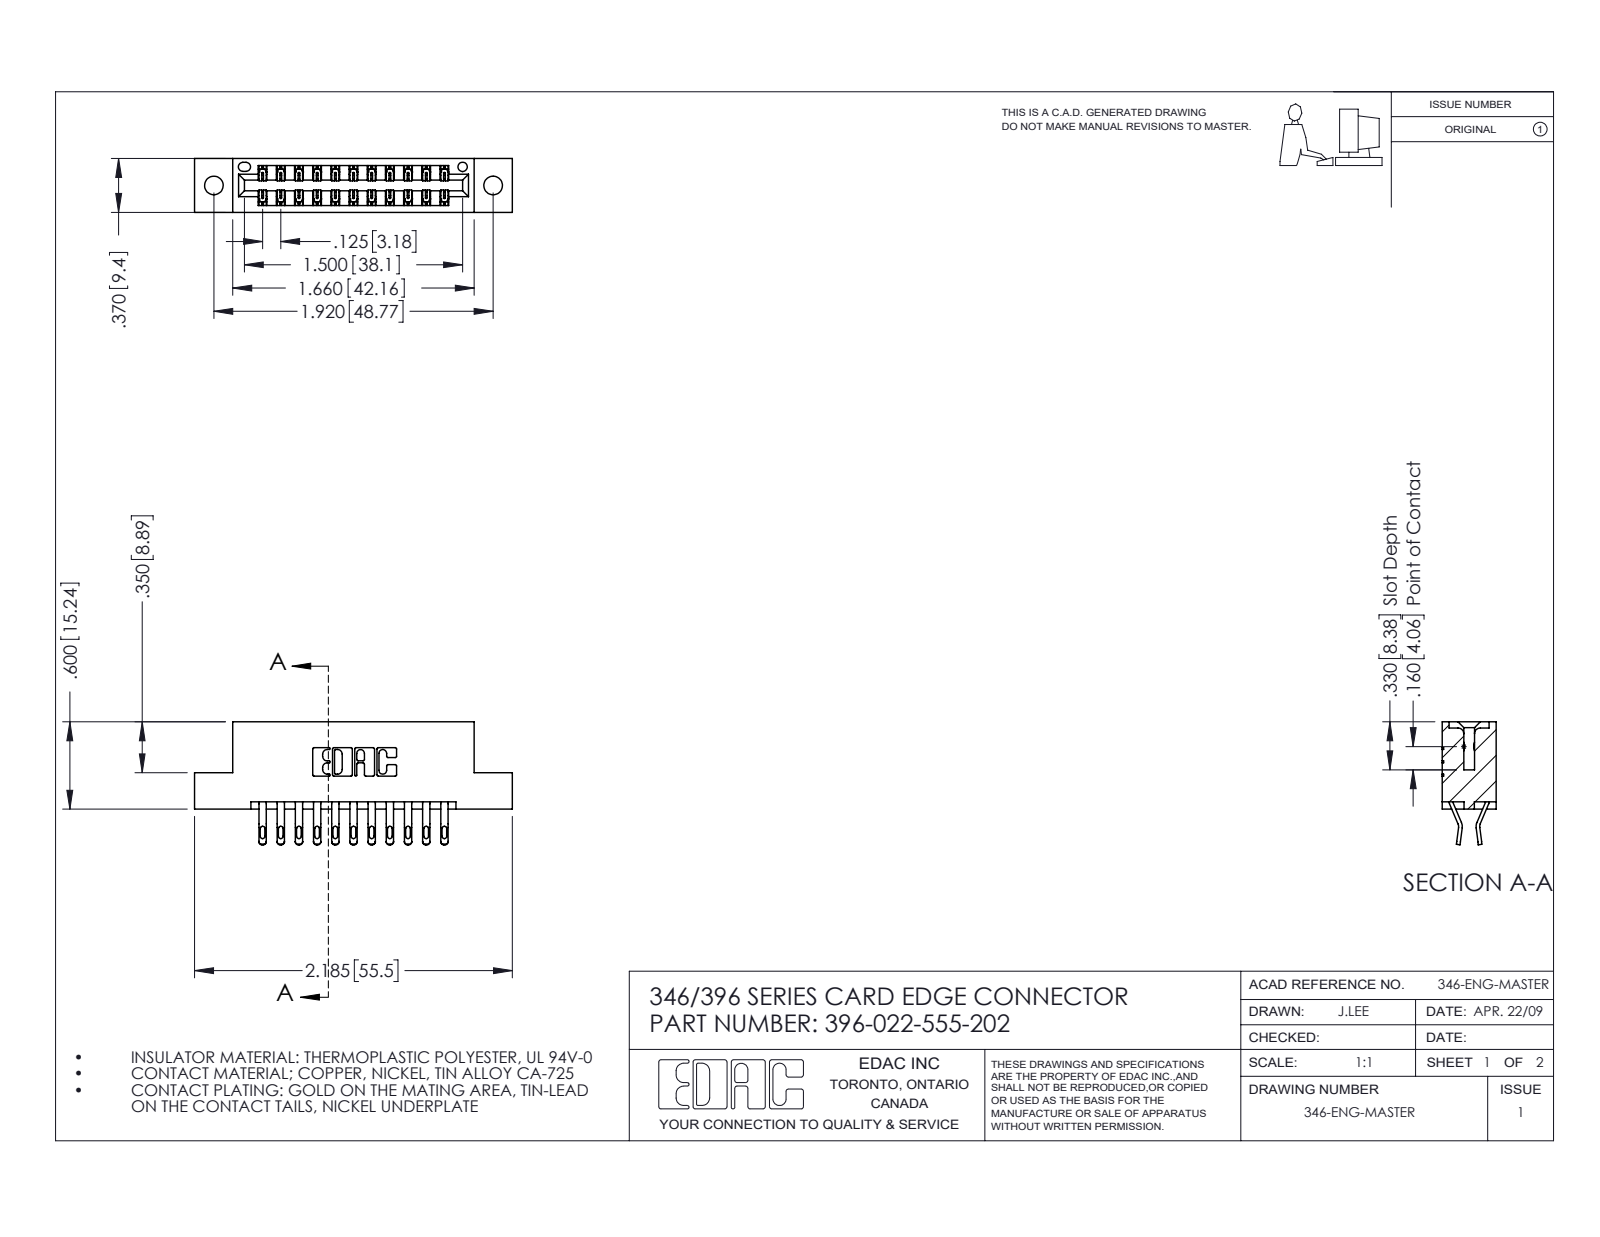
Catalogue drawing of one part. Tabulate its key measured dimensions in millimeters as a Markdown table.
| quantity | value |
| --- | --- |
| part name | 396-022-555-202; 346 Part_Flush Mounting Lugs - 0.128 Dia; 345-292-001_555 Tail |
| STEP written by | SolidWorks 2016 (CONFIG_CONTROL_DESIGN) |
| units | millimeters |
| bodies | 23 solids, 1398 faces (802 planar, 596 cylindrical, 0 other) |
| overall size | 55.5 × 21.5 × 9.4 |
| volume | 5 190 mm³ |
| surface area | 6 619 mm² |
| round holes (diameter × count) | 3.3 × 2, 1.6 × 1 |
| partial cylindrical surfaces (radius × count) | 0.4 × 44, 0.5 × 44, 0.2 × 33, 0.3 × 22, 0.2 × 6, 0.8 × 6, 0.7 × 3, 0.3 × 2 |
| main face-to-face distances | 6.4, 1.2, 8.2, 9.4, 0.6, 1.8, 7.6, 7, 3.8, 5.6 |
| hole center spacings | 6.2, 43.6, 48.8 |
